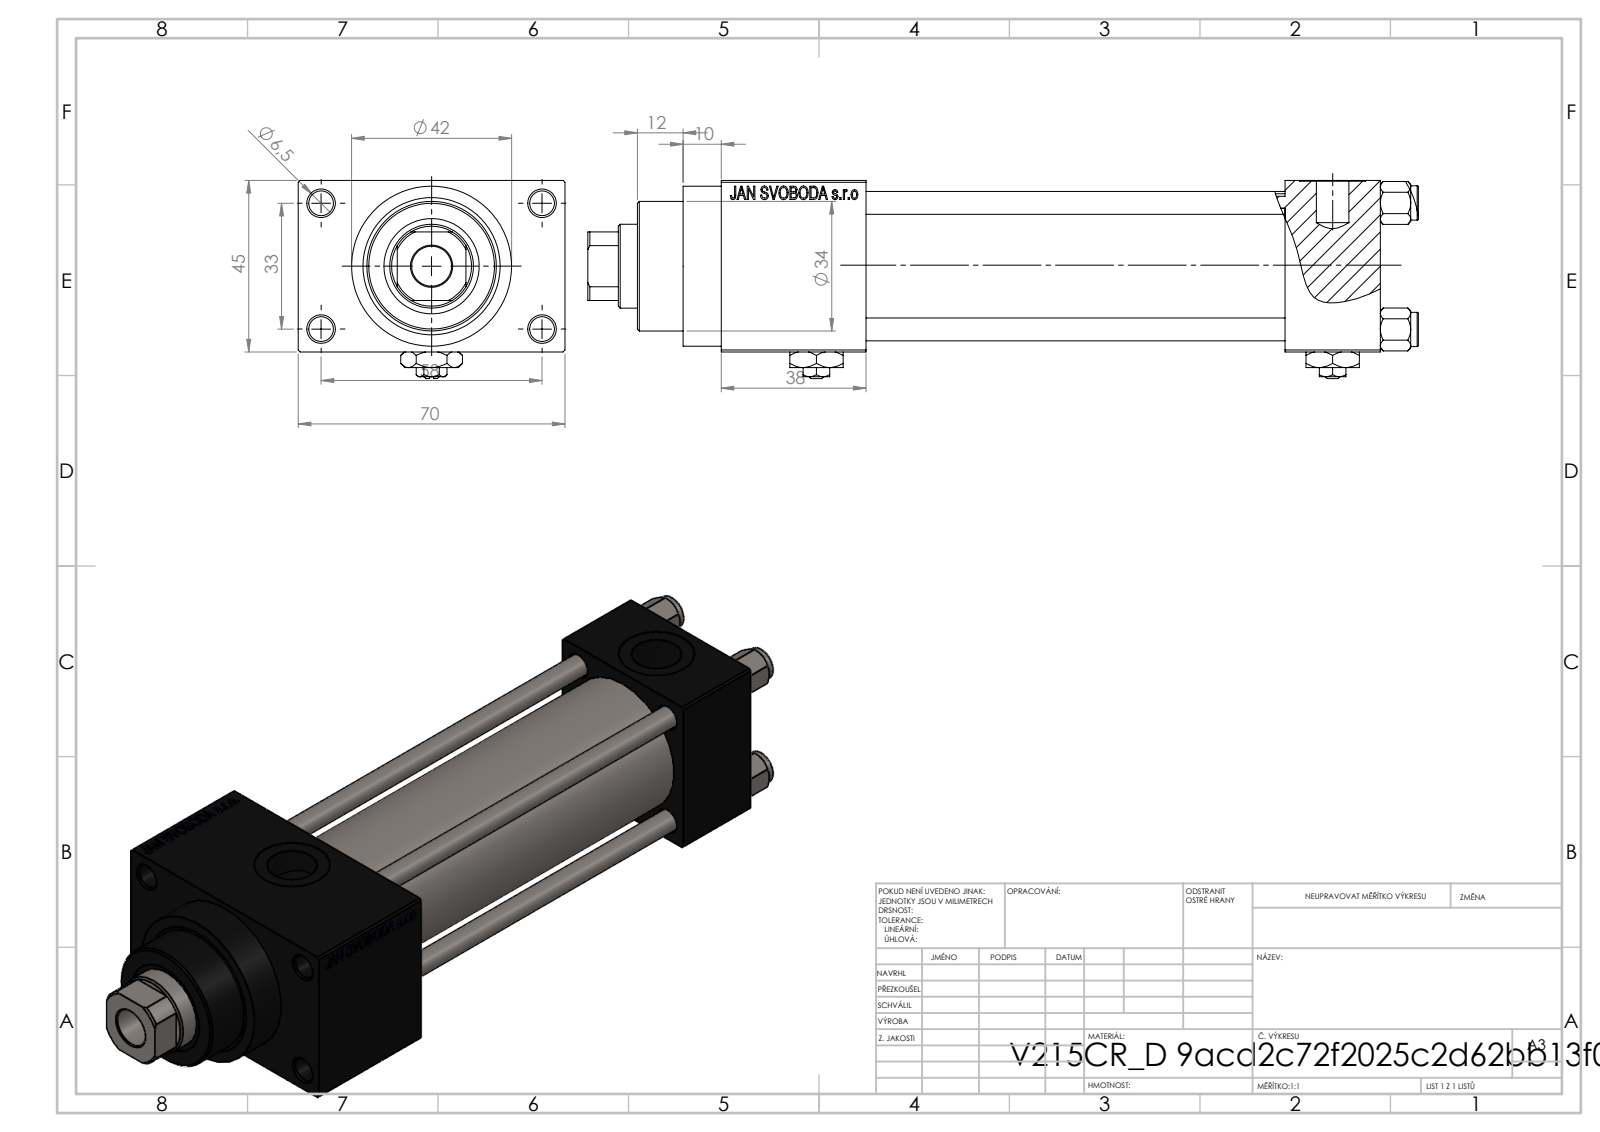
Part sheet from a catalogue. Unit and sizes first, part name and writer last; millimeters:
Units: millimetres
Overall size (bounding box): 218 × 70 × 52
Round holes (diameter × count): ⌀6 ×4, ⌀6.5 ×4, ⌀7 ×2, ⌀13.16 ×2, ⌀20 ×2, ⌀10.5 ×1, ⌀22 ×1, ⌀24 ×1, ⌀25 ×1, ⌀32 ×1, ⌀33 ×1
Round bosses / shafts (diameter × count): ⌀9 ×4, ⌀42 ×1, ⌀38 ×1, ⌀34 ×1
Partial cylindrical surfaces — rounded edges, fillets, slot ends (radius × count): R10.5 ×1
Main face-to-face distances: 45, 25, 12.5, 57.5, 110, 135, 148, 38, 70, 173
Hole centre spacings: 12.4, 23.48, 33.2, 33.37, 35.35, 45.6, 56.35, 33
Volume: 292 633 mm³ · Surface area: 102 977 mm²
Bodies: 13 solids, 1204 faces (542 planar, 100 cylindrical, 562 other)
Part name (STEP PRODUCT): V215CR_D_Body; V215CR_VCP_D; V215_VC_A; NUT_M5_D (+2 more)
STEP written by: SolidWorks 2019 (CONFIG_CONTROL_DESIGN)
